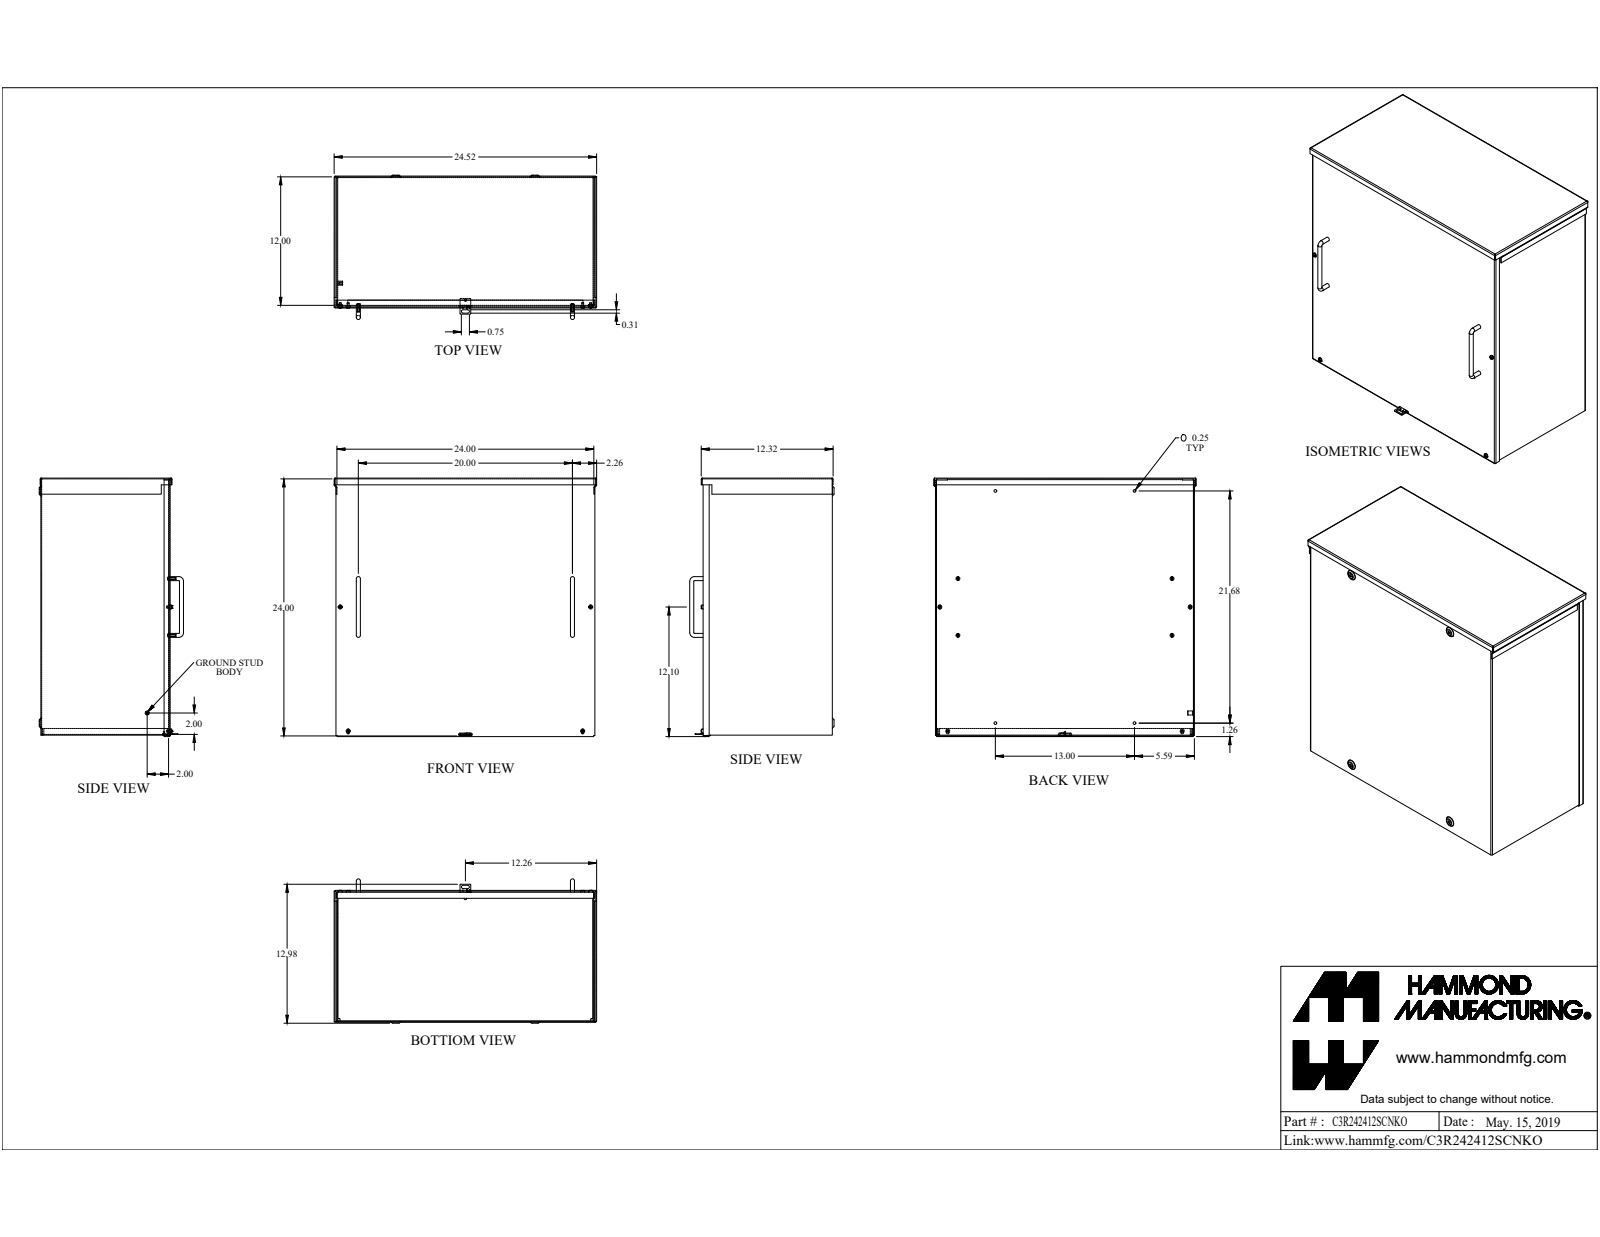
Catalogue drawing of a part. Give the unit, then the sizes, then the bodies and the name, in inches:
Units: inches
Overall size (bounding box): 24.519 × 24.135 × 13.478
Round holes (diameter × count): ⌀0.156 ×5, ⌀0.17 ×4, ⌀0.203 ×4, ⌀0.25 ×4, ⌀0.125 ×1, ⌀0.137 ×1
Round bosses / shafts (diameter × count): ⌀0.375 ×9, ⌀0.19 ×8, ⌀0.367 ×4, ⌀0.375 ×2, ⌀0.125 ×1
Partial cylindrical surfaces — rounded edges, fillets, slot ends (radius × count): R0.036 ×20, R0.108 ×20, R0.109 ×8, R0.125 ×8, R0.156 ×2, R0.029 ×1, R0.086 ×1
Main face-to-face distances: 0.072, 12, 23.928, 11.928, 12.072, 24, 0.072, 23.856, 23.856, 23.928
Hole centre spacings: 20, 0.024, 3.146, 5.3, 8.906, 12.02, 13.936, 18.42
Volume: 176.6 in³ · Surface area: 4 987 in²
Bodies: 17 solids, 453 faces (287 planar, 106 cylindrical, 60 other)
Part name (STEP PRODUCT): C3R242412SCNKO
STEP written by: SolidWorks 2019 (AUTOMOTIVE_DESIGN)
